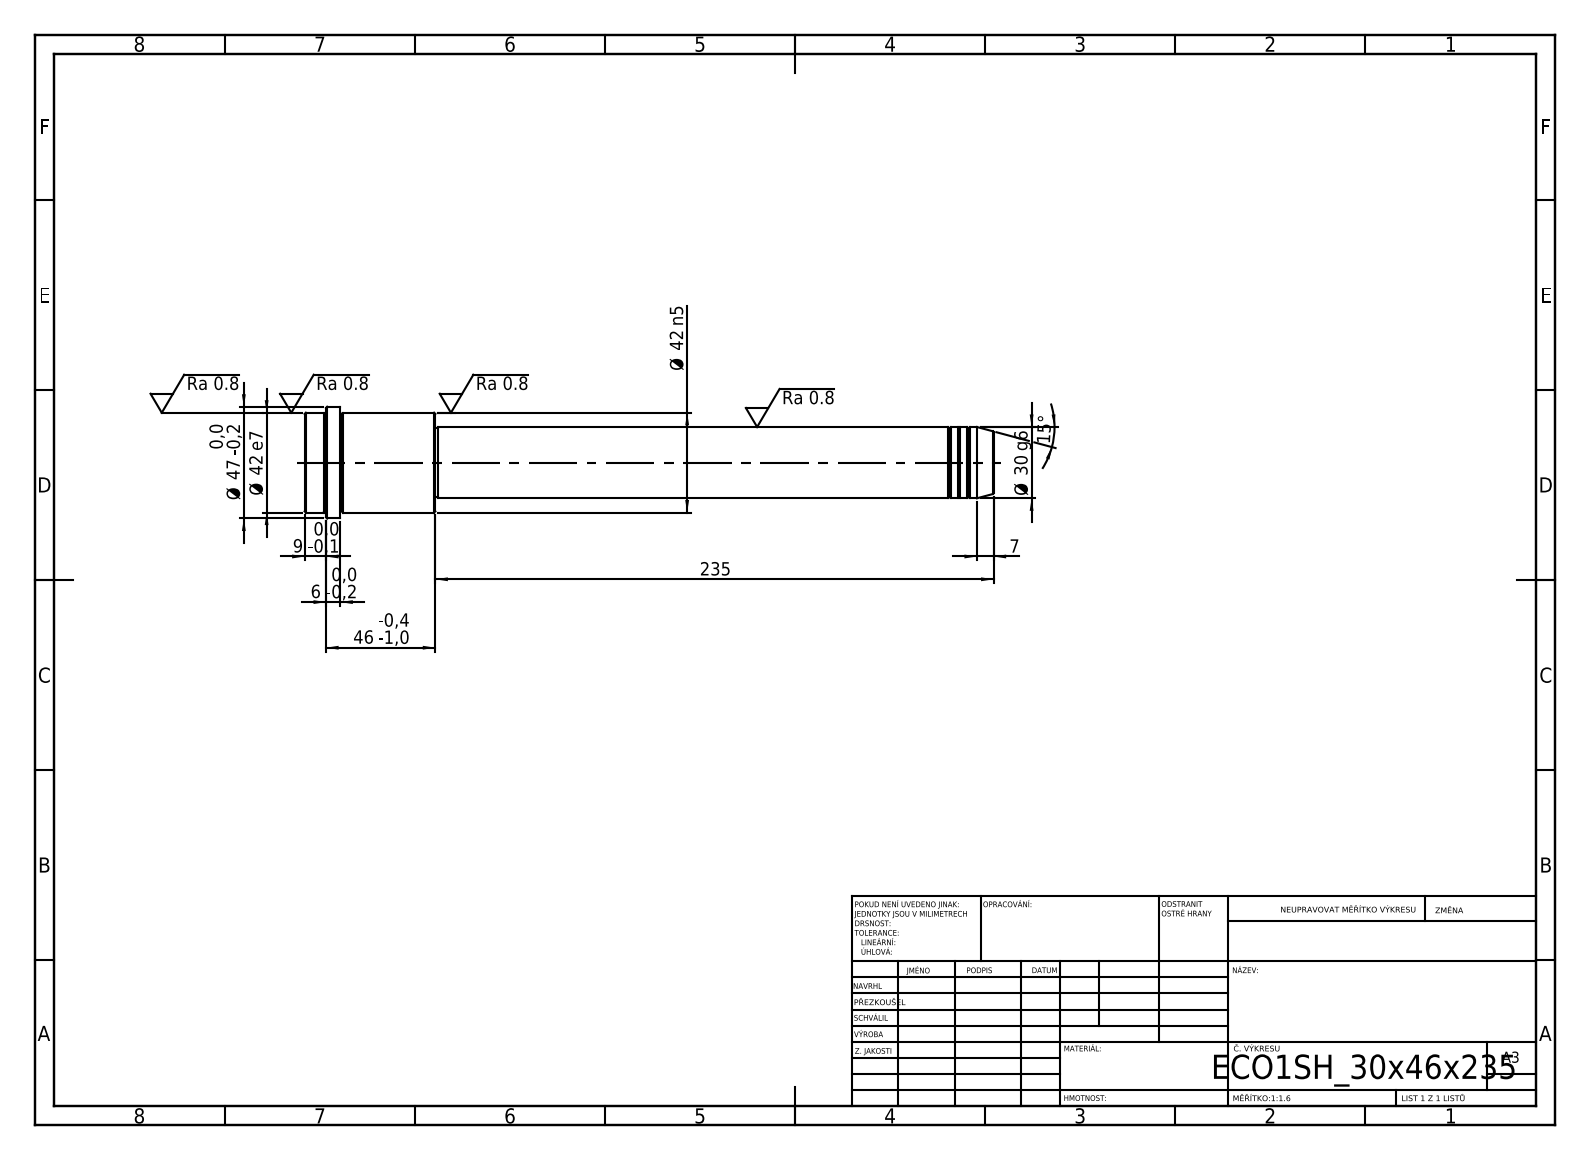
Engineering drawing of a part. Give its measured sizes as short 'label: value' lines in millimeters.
written by: SolidWorks 2019 (CONFIG_CONTROL_DESIGN)
unit: mm
bodies: 1 solid, 52 faces (6 planar, 16 cylindrical, 30 other)
size: 290 × 47 × 47
volume: 243 503 mm³; area: 33 039 mm²
bosses: 1× ⌀47, 1× ⌀42, 1× ⌀30, 1× ⌀29
face distances: 55, 235, 290, 275, 40, 15, 281, 46, 6, 9
